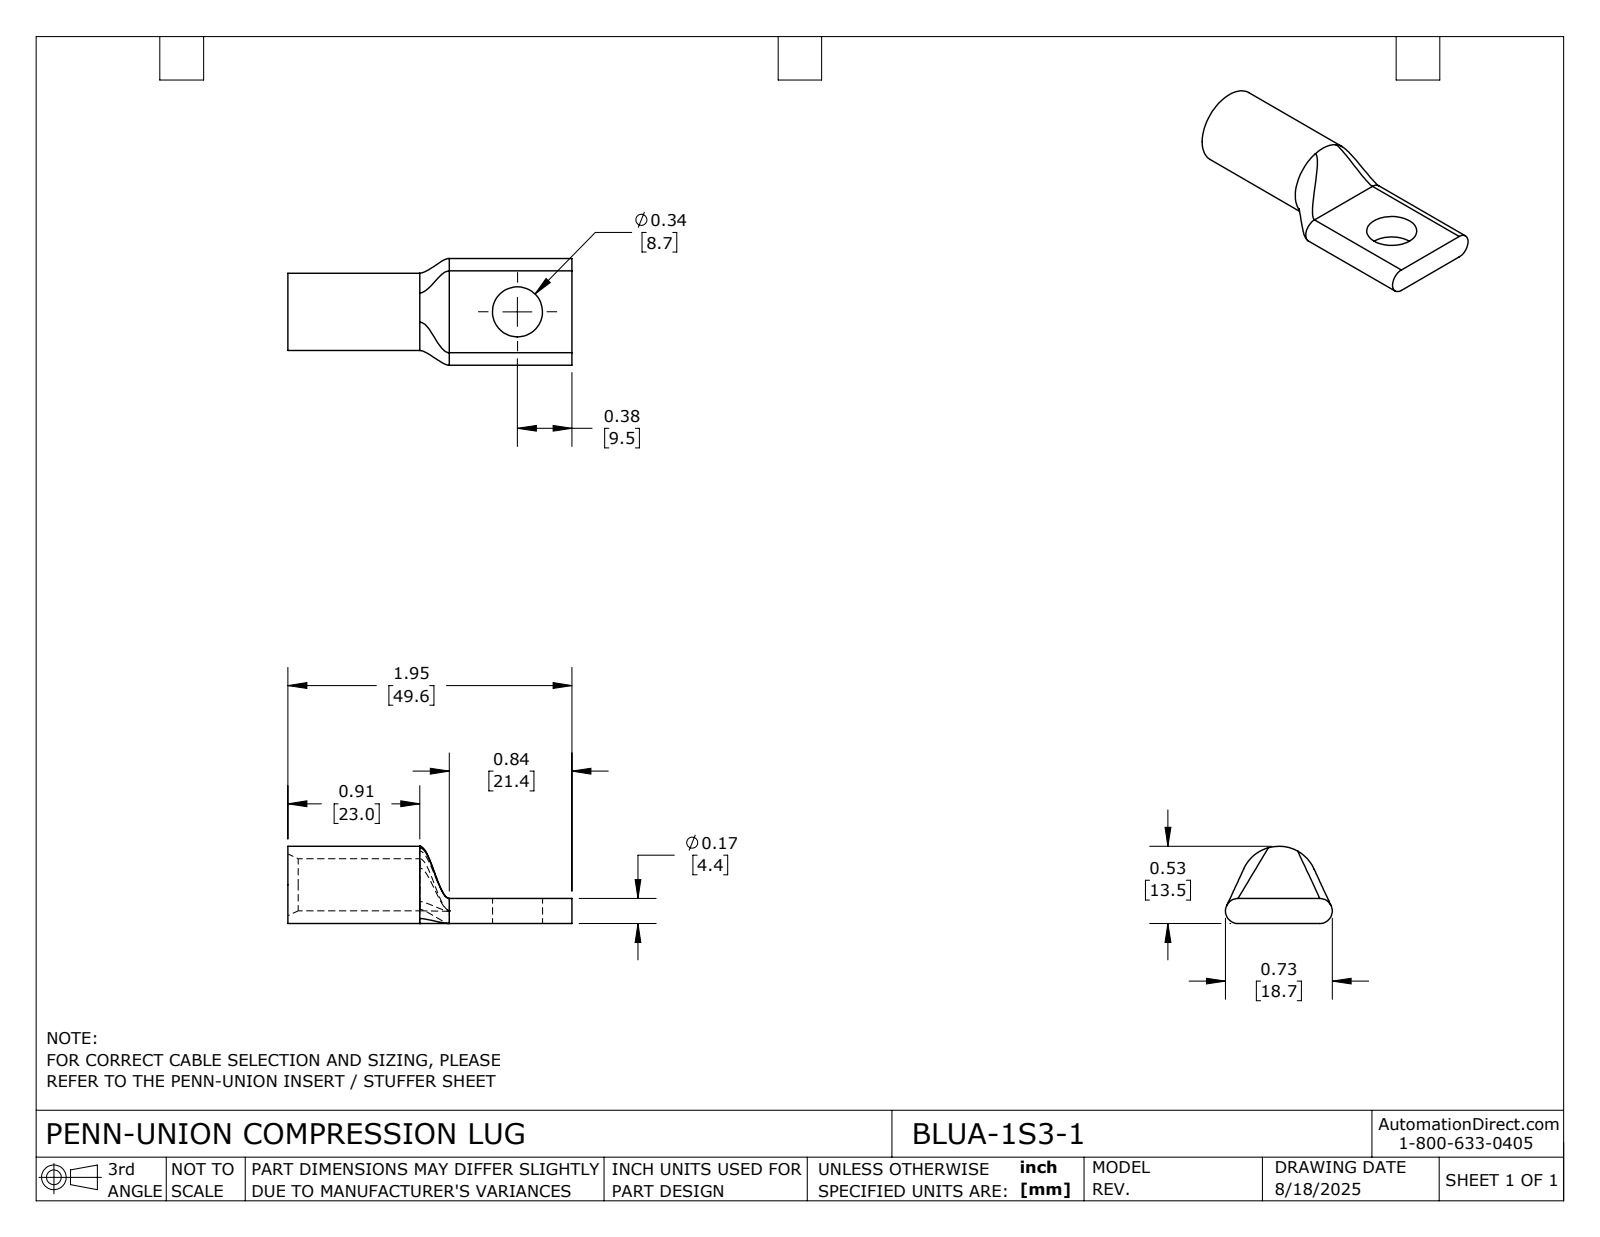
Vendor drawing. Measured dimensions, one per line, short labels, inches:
name: BLUA-1S3-1
written by: SolidWorks 2024 (CONFIG_CONTROL_DESIGN)
unit: in
bodies: 1 solid, 24 faces (5 planar, 9 cylindrical, 10 other)
size: 1.953 × 0.734 × 0.531
volume: 0.217 in³; area: 4.923 in²
holes: 1× ⌀0.344, 1× ⌀0.358
bosses: 1× ⌀0.531
rounds: 2× R0.086
face distances: 0.172, 1.953, 1.109, 0.844
